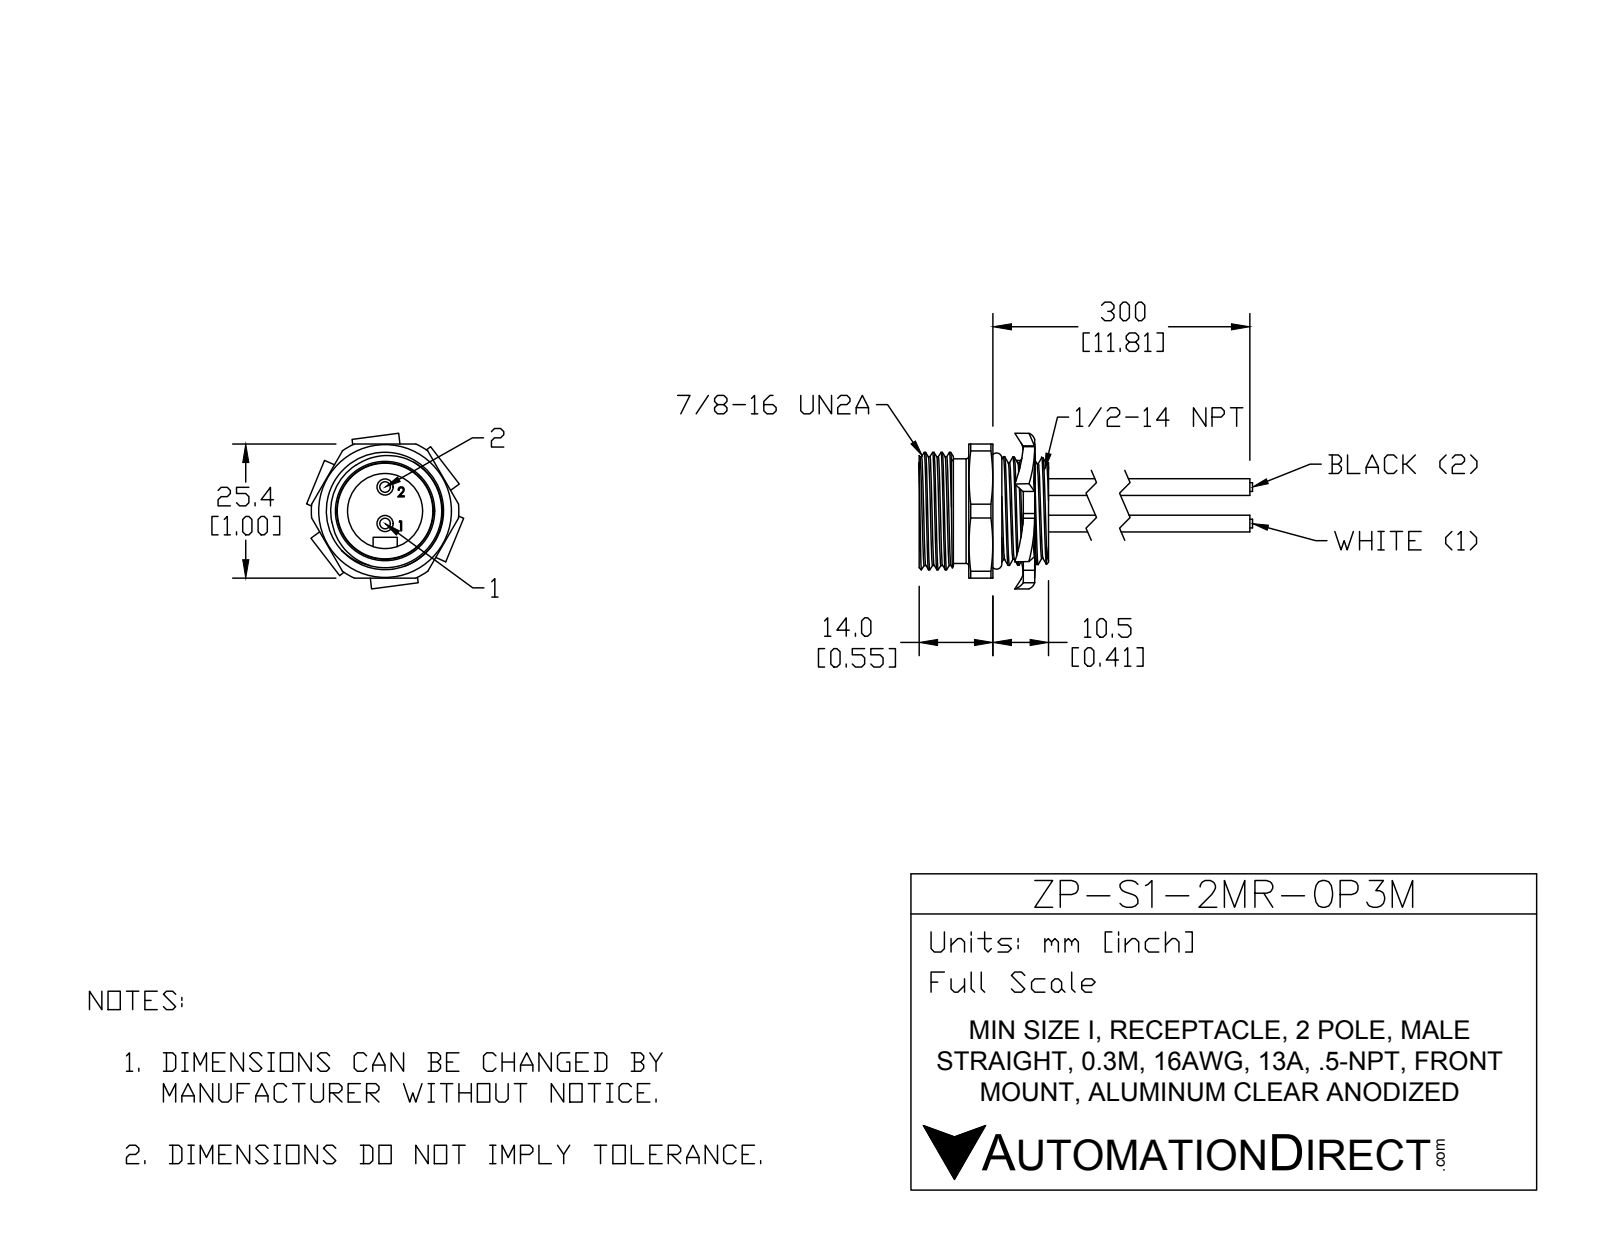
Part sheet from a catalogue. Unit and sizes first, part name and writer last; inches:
Units: inches
Overall size (bounding box): 6.713 × 1.1 × 1
Round holes (diameter × count): ⌀0.547 ×1, ⌀0.56 ×1, ⌀0.72 ×1
Round bosses / shafts (diameter × count): ⌀0.125 ×2, ⌀0.12 ×2, ⌀0.079 ×2, ⌀0.875 ×1, ⌀0.811 ×1, ⌀0.78 ×1, ⌀0.716 ×1, ⌀0.065 ×1
Partial cylindrical surfaces — rounded edges, fillets, slot ends (radius × count): R0.09 ×1, R0.55 ×1
Main face-to-face distances: 0.353, 0.18, 0.533, 1, 0.057, 0.237, 0.59, 0.652, 0.595, 0.415
Bodies: 0 solids, 120 faces (25 planar, 54 cylindrical, 41 other)
Part name (STEP PRODUCT): MIN-2MR-ZZ
STEP written by: SolidWorks 2008 (AUTOMOTIVE_DESIGN)
